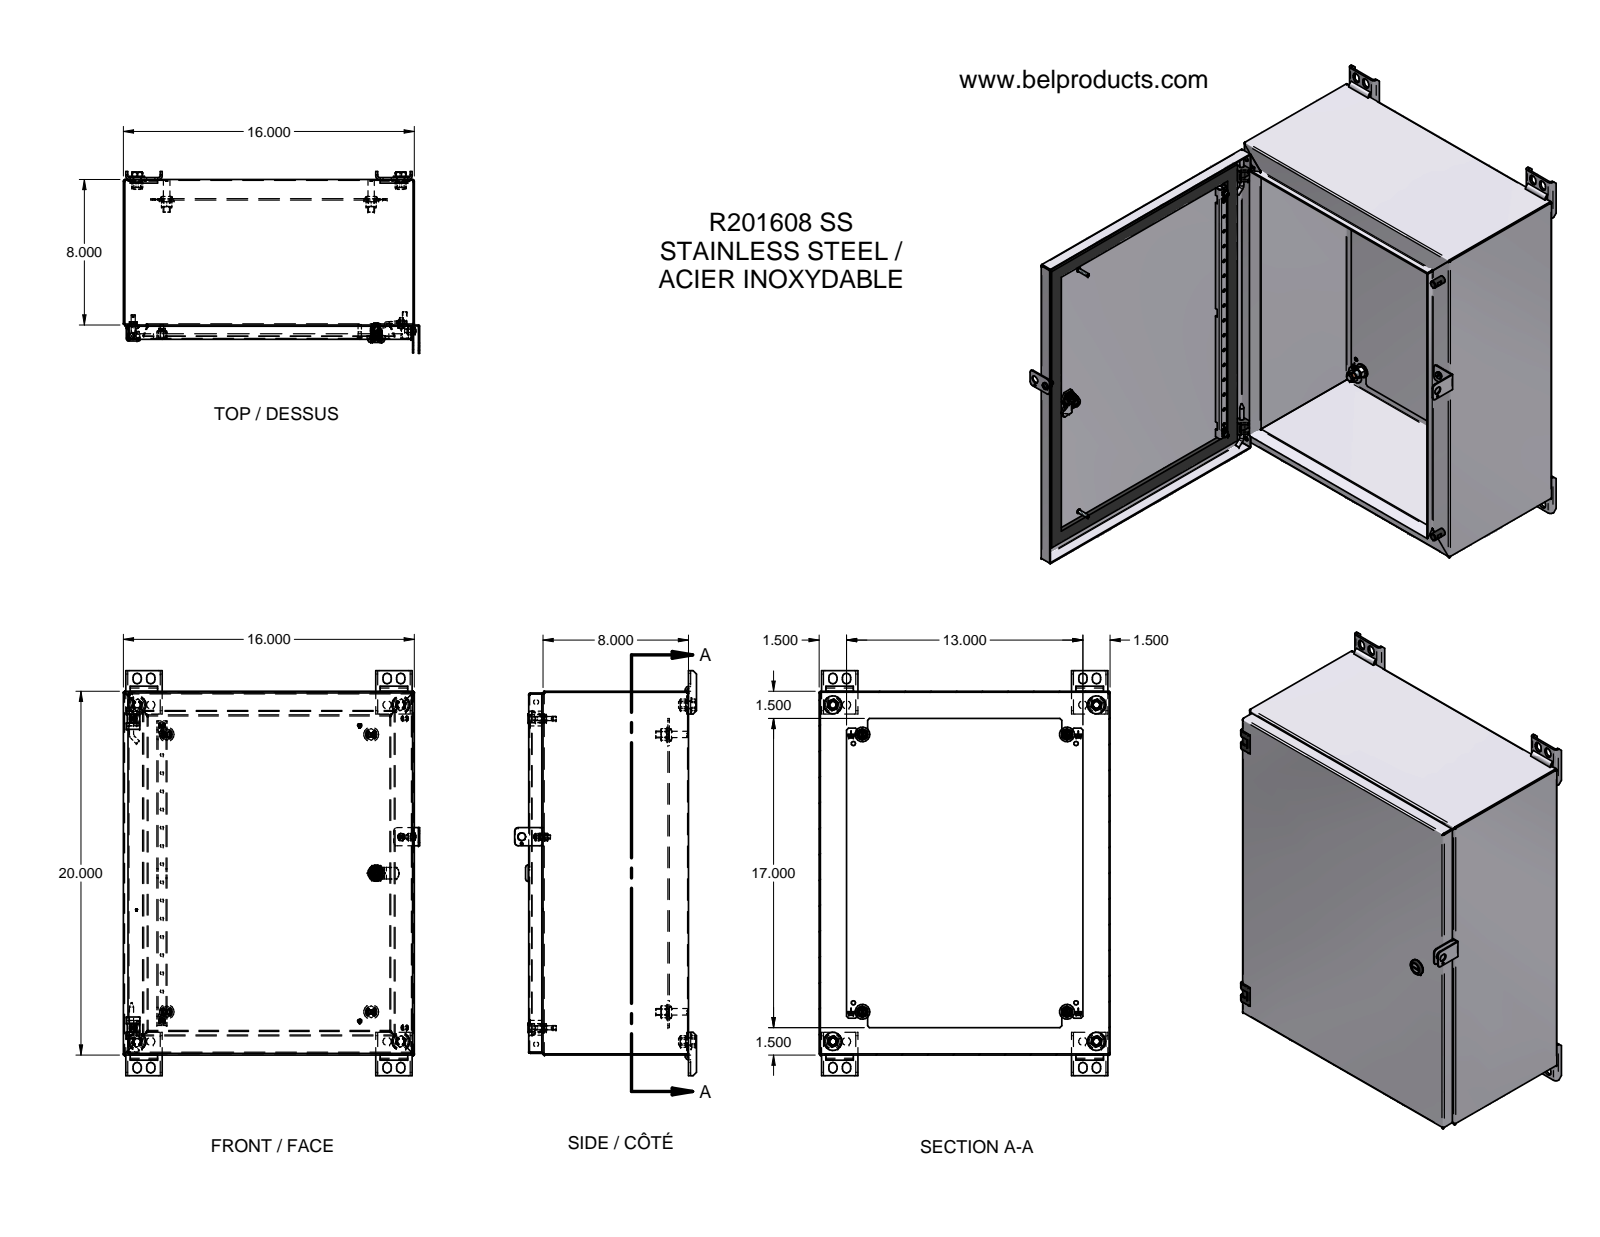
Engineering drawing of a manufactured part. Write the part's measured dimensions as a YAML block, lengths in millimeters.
part_name: "0.375 DIA; METAL; CAOUTCHOUC; LOCK AVEC TOURNEVIS TYPE 4-12 SANS CAME (+8 more)"
step_written_by: "Unknown (AUTOMOTIVE_DESIGN)"
units: millimeters
bodies: {solids: 79, faces: 3080, planar: 1800, cylindrical: 522, other: 758}
overall_size: [565.56, 413.56, 253.87]
volume: 1930000
surface_area: 2255000
round_holes:
  - {diameter: 4.68, count: 16}
  - {diameter: 3.17, count: 10}
  - {diameter: 9.53, count: 8}
  - {diameter: 10.31, count: 8}
  - {diameter: 11.58, count: 8}
  - {diameter: 0.35, count: 6}
  - {diameter: 4.04, count: 4}
  - {diameter: 5.99, count: 4}
  - {diameter: 6.73, count: 4}
  - {diameter: 9.02, count: 4}
  - {diameter: 10.54, count: 4}
  - {diameter: 12.7, count: 4}
round_bosses_or_shafts:
  - {diameter: 3.02, count: 10}
  - {diameter: 20.62, count: 8}
  - {diameter: 4.83, count: 5}
  - {diameter: 16.19, count: 4}
  - {diameter: 8.97, count: 4}
  - {diameter: 6.5, count: 4}
  - {diameter: 0.79, count: 4}
  - {diameter: 0.51, count: 4}
partial_cylinders:
  - {radius: 0.2, count: 84}
  - {radius: 0.81, count: 22}
  - {radius: 0.3, count: 18}
  - {radius: 2.34, count: 18}
  - {radius: 5.79, count: 16}
  - {radius: 4.76, count: 12}
  - {radius: 9.53, count: 12}
  - {radius: 0.25, count: 8}
face_to_face_distances: [1.52, 221.78, 220.26, 404.88, 223.3, 506.48, 194.57, 193.05, 27.21, 28.73]
hole_center_spacings: [25.4, 50.8, 76.2, 101.6, 127, 152.4, 177.8, 203.2]
